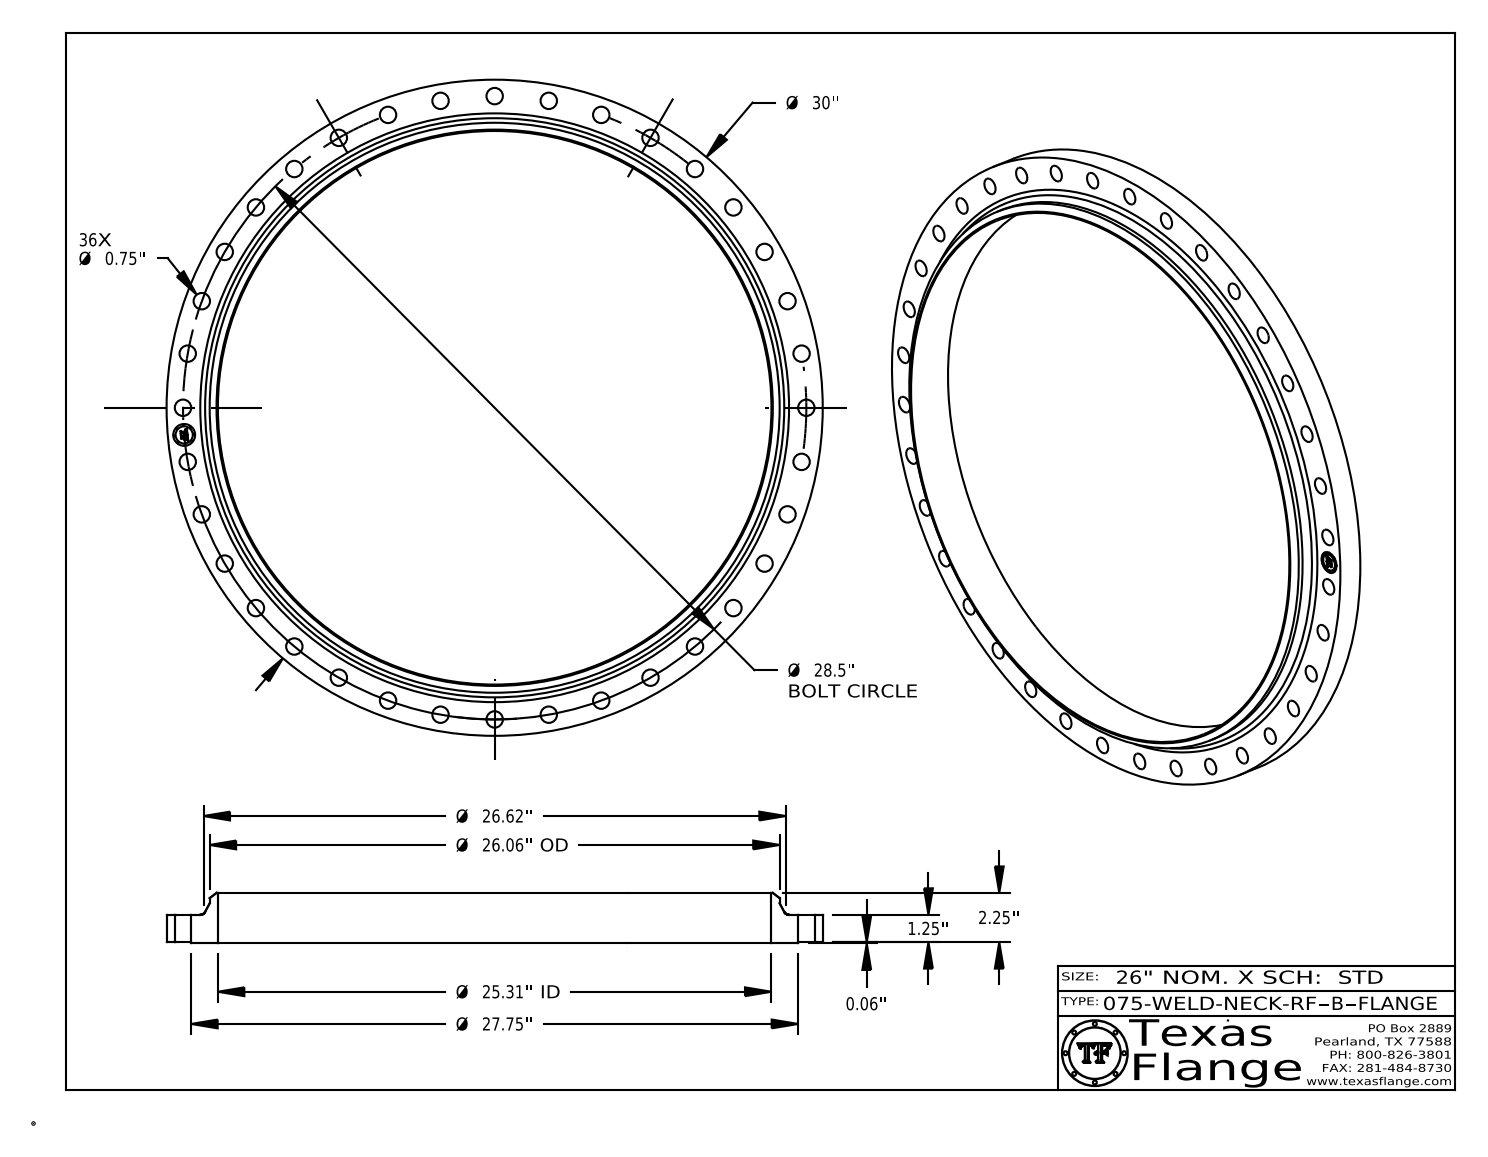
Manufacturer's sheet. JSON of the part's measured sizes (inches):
{"part_name": "075-WELD-NECK-RF, Series B", "step_written_by": "CATIA V5 STEP AP214 (AUTOMOTIVE_DESIGN)", "units": "inches", "bodies": {"solids": 1, "faces": 475, "planar": 369, "cylindrical": 100, "other": 6}, "overall_size": [30, 30, 2.313], "volume_in3": 274.8, "surface_area_in2": 838.5, "round_holes": [[0.75, 36], [1, 1], [25.31, 1]], "round_bosses_or_shafts": [[0.061, 8], [30, 1], [27.75, 1], [26.06, 1], [0.788, 1]], "face_to_face_distances": [1.313, 0.063, 1.25, 2.313, 2.25, 1, 0.015, 1.298, 1.235, 1.015], "hole_center_spacings": [14.25, 25.83, 9.748, 21.832, 12.044, 2.484, 24.682, 16.347]}
